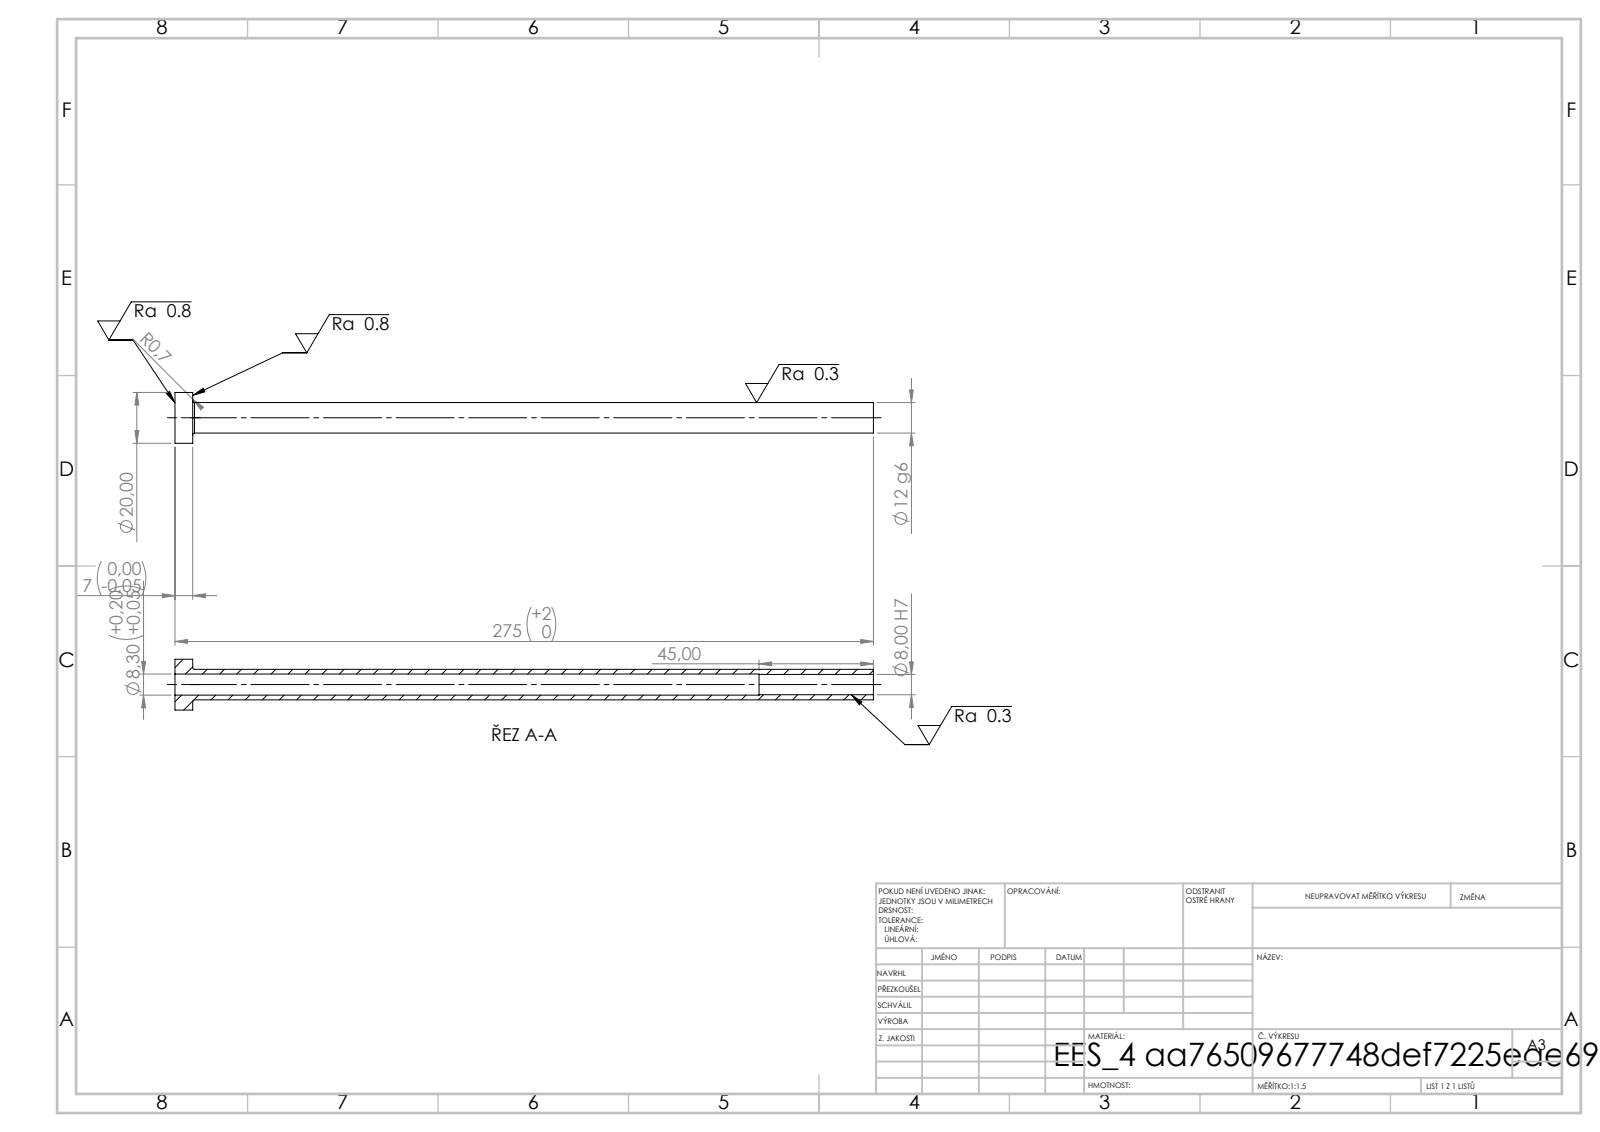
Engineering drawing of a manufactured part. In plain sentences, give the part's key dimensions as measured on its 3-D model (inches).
Its 3-D file was written by "SolidWorks 2019 (CONFIG_CONTROL_DESIGN)". It is 1 solid with 14 faces: 4 planar, 8 cylindrical and 2 other. Overall it measures 10.827 by 0.787 by 0.787 inches. Its volume is 1.087 cubic inches and its surface area 28.19 square inches. Round holes: 1 of diameter 0.315, 1 of diameter 0.327. Round bosses or shafts: 1 of diameter 0.787, 1 of diameter 0.472. The main face-to-face distances are 0.276, 10.827, 10.551, 9.055, 8.78, 1.772.
